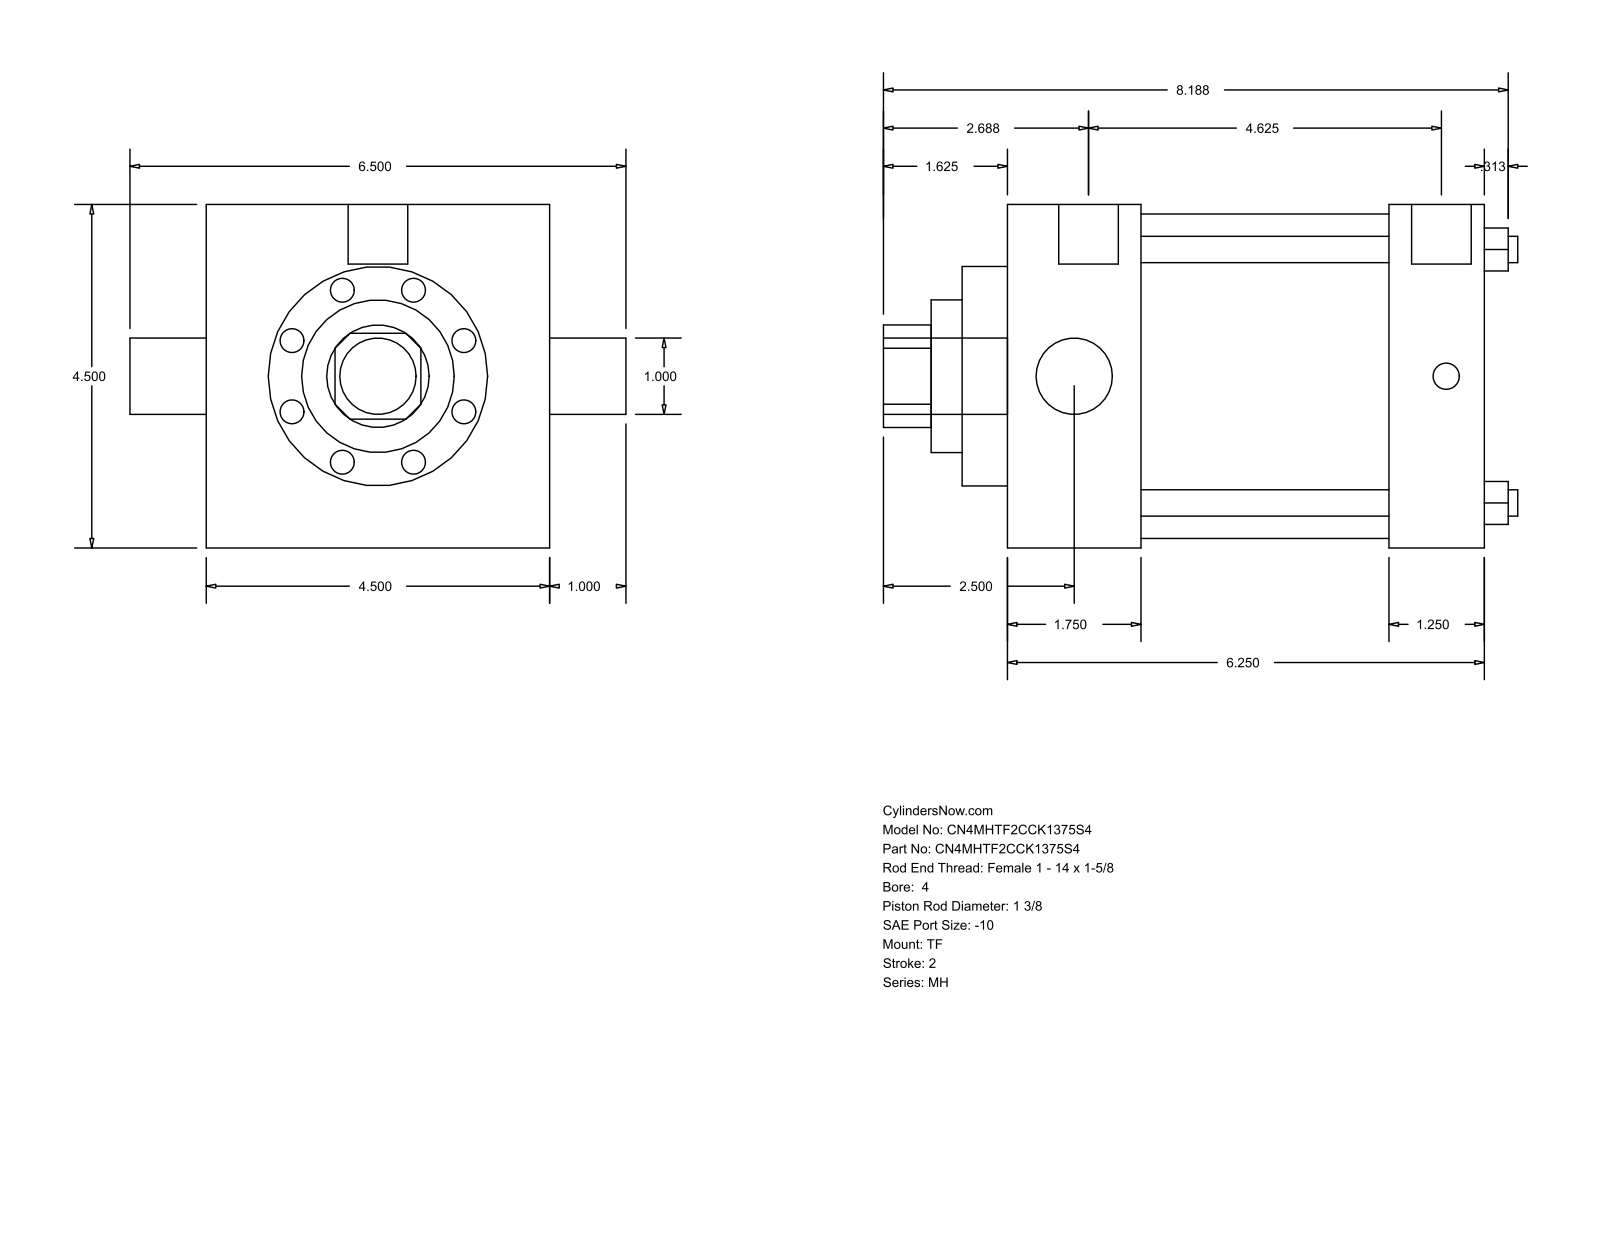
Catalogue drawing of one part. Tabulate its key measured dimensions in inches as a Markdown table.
| quantity | value |
| --- | --- |
| part name | MH_TF__0400_1.375 |
| STEP written by | GSSL Pune (CONFIG_CONTROL_DESIGN) |
| units | inches |
| bodies | 0 solids, 86 faces (61 planar, 25 cylindrical, 0 other) |
| overall size | 8.313 × 6.5 × 4.5 |
| round holes (diameter × count) | 0.345 × 4, 1 × 1, 1.375 × 1, 2 × 1, 2.875 × 1, 4.25 × 1 |
| round bosses / shafts (diameter × count) | 0.344 × 3, 0.781 × 2, 1 × 1 |
| partial cylindrical surfaces (radius × count) | 0.672 × 1 |
| main face-to-face distances | 4.5, 6.25, 1.75, 4.5, 5, 3.25, 1.25, 0.594, 2.344, 5.594 |
| hole center spacings | 2.347, 3.32, 4.695 |
